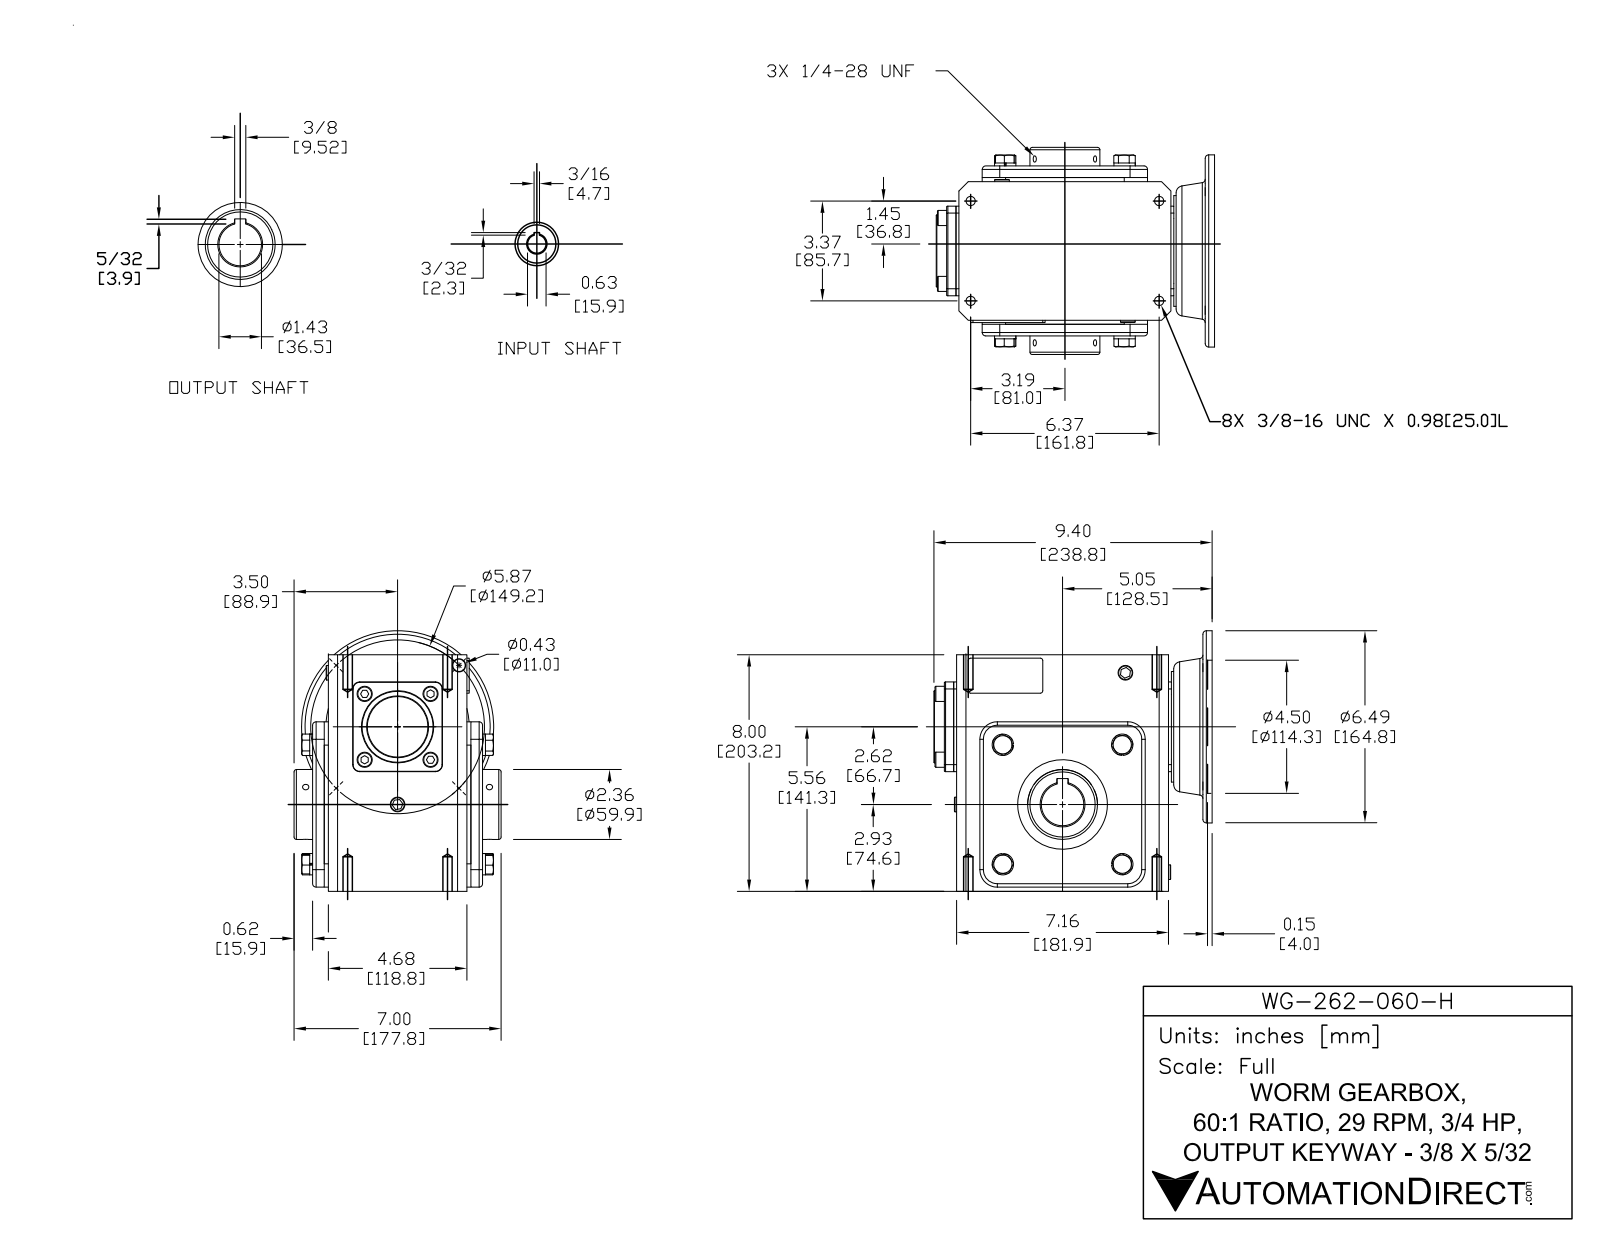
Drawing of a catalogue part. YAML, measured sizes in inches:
part_name: "WG-262-060-H"
step_written_by: "SolidWorks 2015 (CONFIG_CONTROL_DESIGN)"
units: inches
bodies: {solids: 37, faces: 558, planar: 306, cylindrical: 156, other: 96}
overall_size: [9.409, 8.811, 7]
volume: 310.4
surface_area: 663.9
round_holes:
  - {diameter: 0.213, count: 6}
  - {diameter: 0.313, count: 4}
  - {diameter: 0.406, count: 4}
  - {diameter: 0.591, count: 1}
  - {diameter: 0.625, count: 1}
  - {diameter: 1.437, count: 1}
  - {diameter: 1.457, count: 1}
  - {diameter: 2.362, count: 1}
  - {diameter: 3.031, count: 1}
  - {diameter: 3.819, count: 1}
  - {diameter: 4.5, count: 1}
round_bosses_or_shafts:
  - {diameter: 0.724, count: 4}
  - {diameter: 0.512, count: 4}
  - {diameter: 6.496, count: 1}
  - {diameter: 3.74, count: 1}
  - {diameter: 2.441, count: 1}
  - {diameter: 2.047, count: 1}
  - {diameter: 1.181, count: 1}
  - {diameter: 1.142, count: 1}
partial_cylinders:
  - {radius: 0.079, count: 8}
  - {radius: 0.118, count: 8}
  - {radius: 0.236, count: 4}
  - {radius: 0.591, count: 4}
  - {radius: 0.787, count: 4}
  - {radius: 0.02, count: 2}
  - {radius: 0.039, count: 2}
face_to_face_distances: [4.961, 0.394, 0.098, 5.217, 5.354, 0.138, 4.823, 0.531, 7.264, 8]
hole_center_spacings: [2.937, 3.489, 4.154, 5.757, 6.213, 2.148, 3.375, 5.14]
